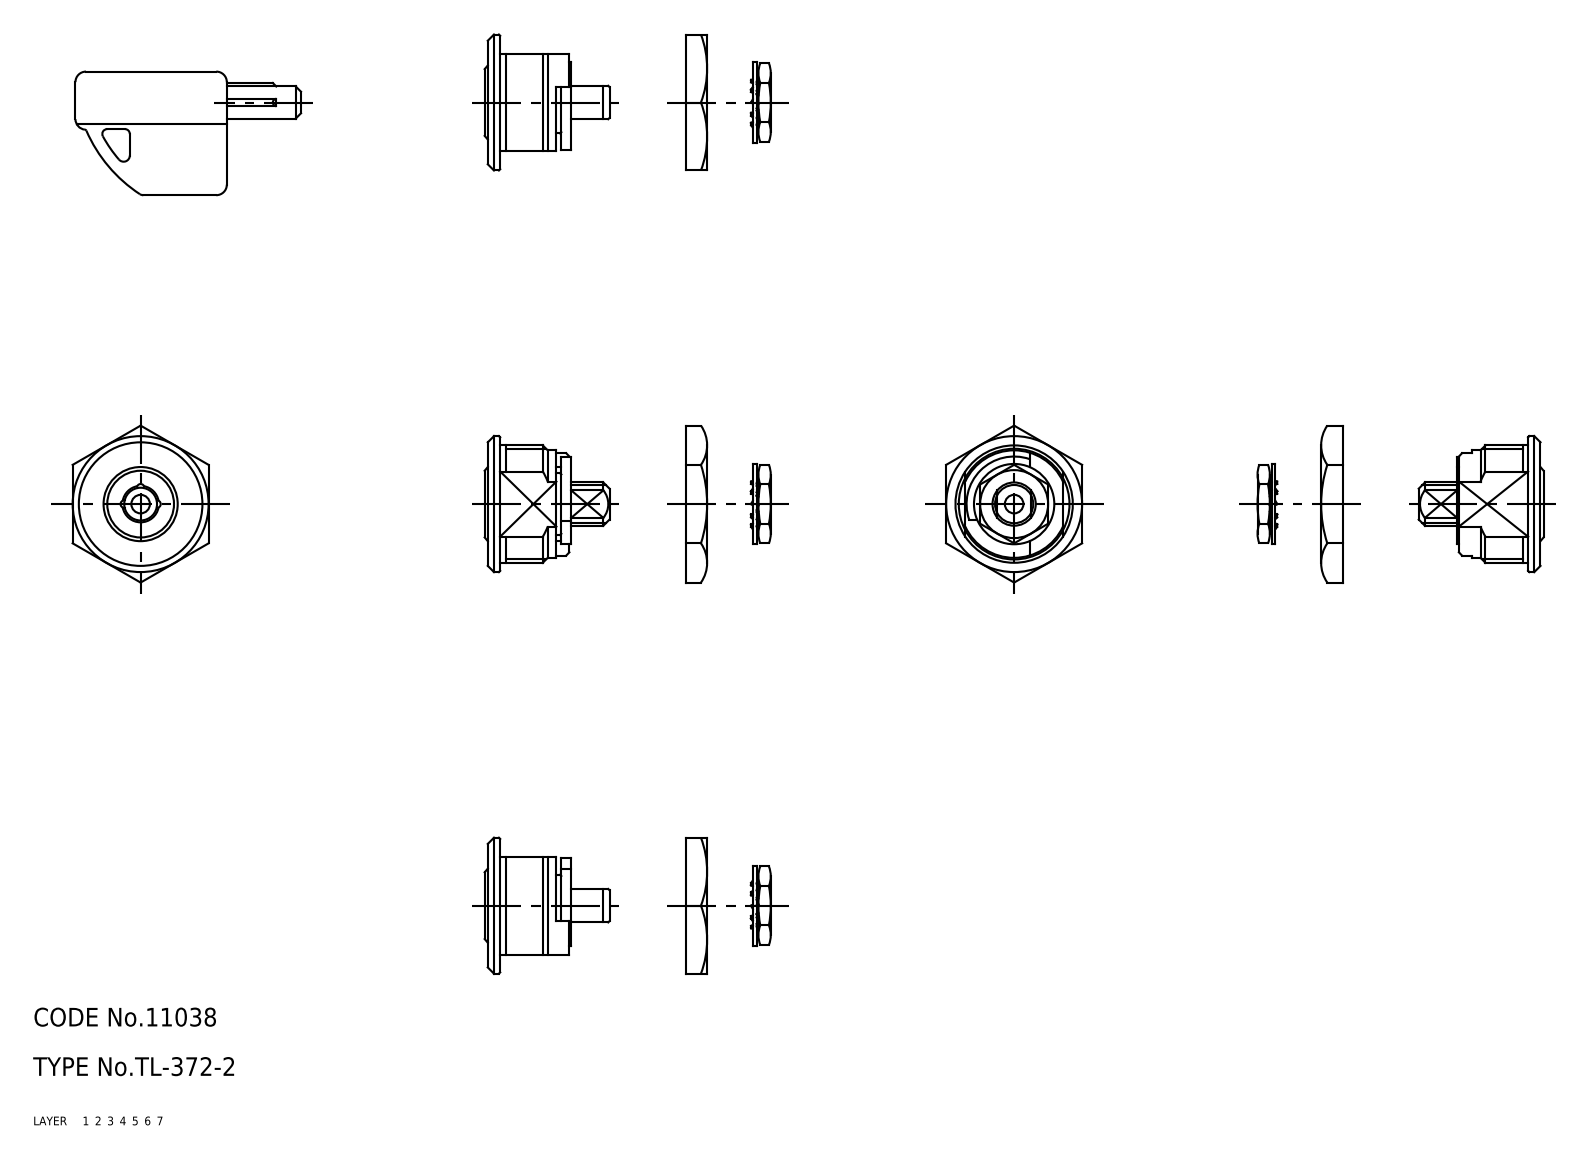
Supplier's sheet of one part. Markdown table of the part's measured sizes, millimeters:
| quantity | value |
| --- | --- |
| part name | 67116737; 67116750; 67116763; 67116776 (+2 more) |
| STEP written by | CADfix (AUTOMOTIVE_DESIGN) |
| units | millimeters |
| bodies | 6 solids, 157 faces (0 planar, 0 cylindrical, 157 other) |
| overall size | 106.7 × 27.7 × 22 |
| volume | 6 578 mm³ |
| surface area | 5 459 mm² |
